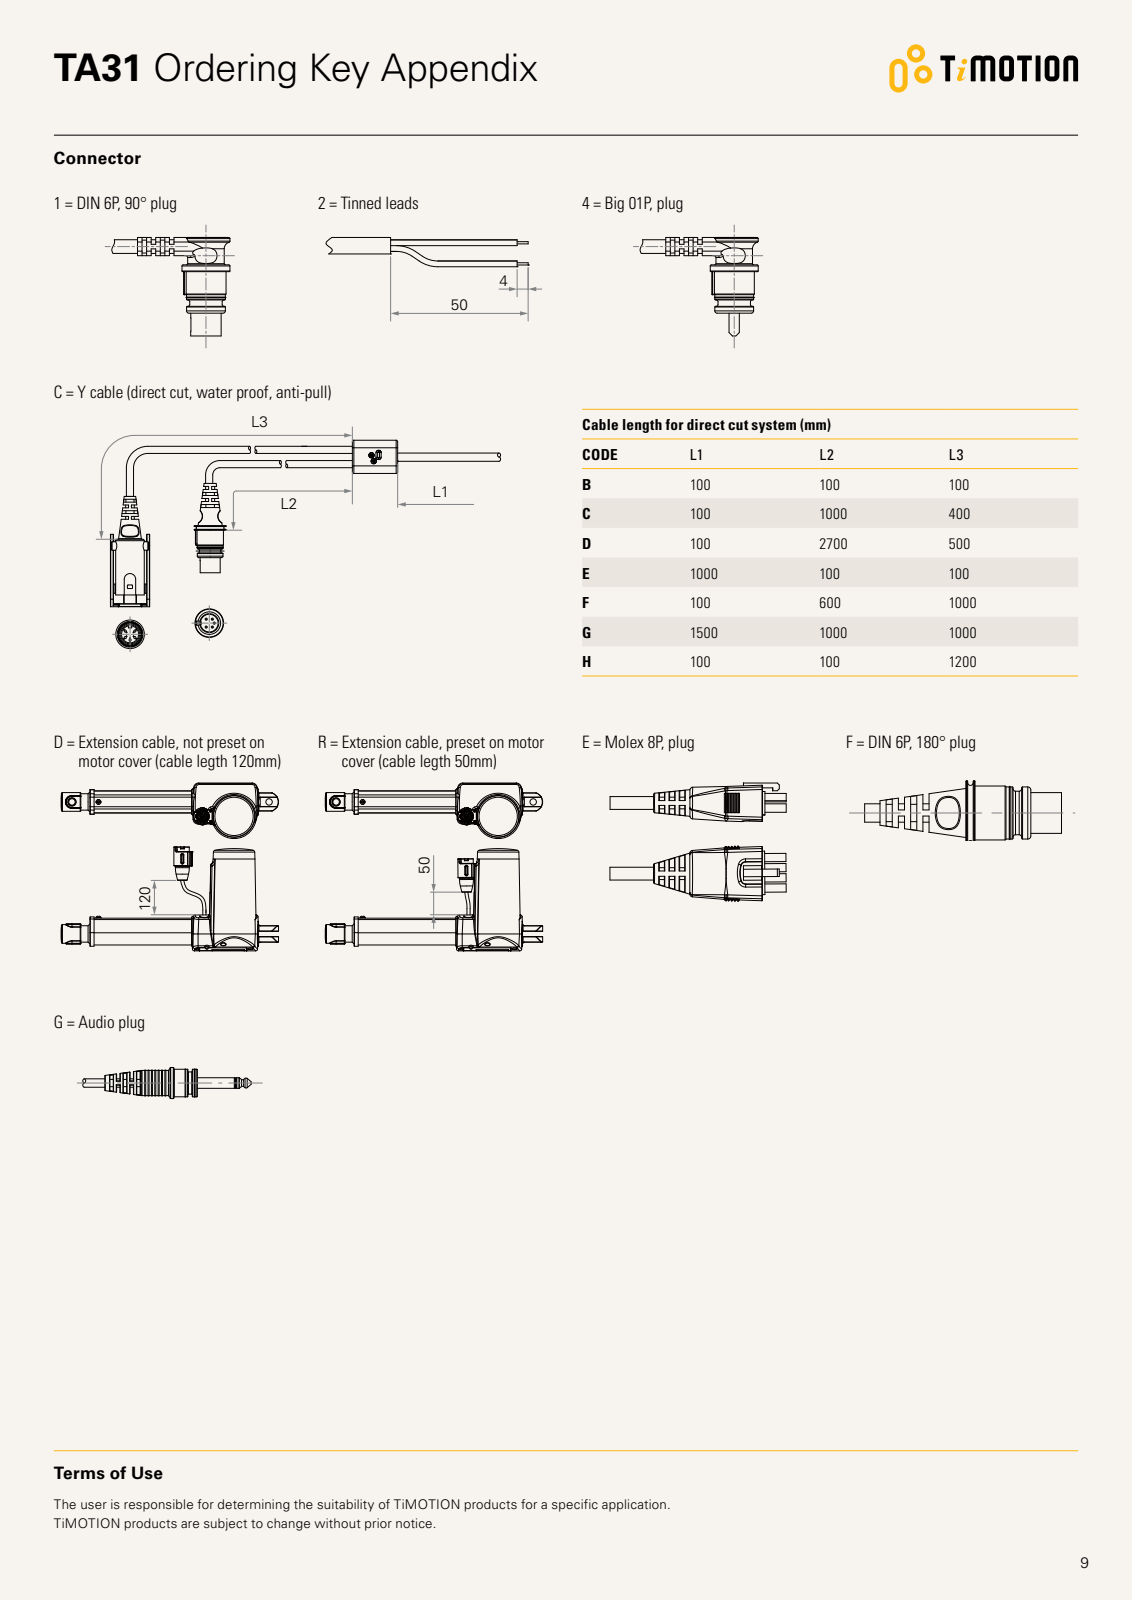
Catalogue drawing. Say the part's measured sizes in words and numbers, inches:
The part is named "TA31-A". Its 3-D file was written by "SolidWorks 2015 (CONFIG_CONTROL_DESIGN)". It is 1 solid with 503 faces: 156 planar, 146 cylindrical and 201 other. Overall it measures 13.933 by 6.386 by 3.469 inches. Its volume is 61.63 cubic inches and its surface area 139.8 square inches. Round holes: 12 of diameter 0.157, 5 of diameter 0.307, 2 of diameter 0.402, 1 of diameter 0.13. Round bosses or shafts: 1 of diameter 1.181, 1 of diameter 1.024, 1 of diameter 0.307, 1 of diameter 0.197. Partial cylindrical surfaces (rounded edges, fillets, slot ends): 30 of radius 0.02, 12 of radius 0.039, 6 of radius 0.118, 3 of radius 0.157, 3 of radius 0.315, 2 of radius 0.098, 2 of radius 0.236, 2 of radius 0.276. The main face-to-face distances are 2.041, 0.823, 1.219, 0.323, 0.896, 1.146, 0.118, 0.827, 0.669, 0.256. The hole center spacings are 0.243, 0.394, 0.637, 0.749, 0.463, 0.787, 0.463, 0.252.
